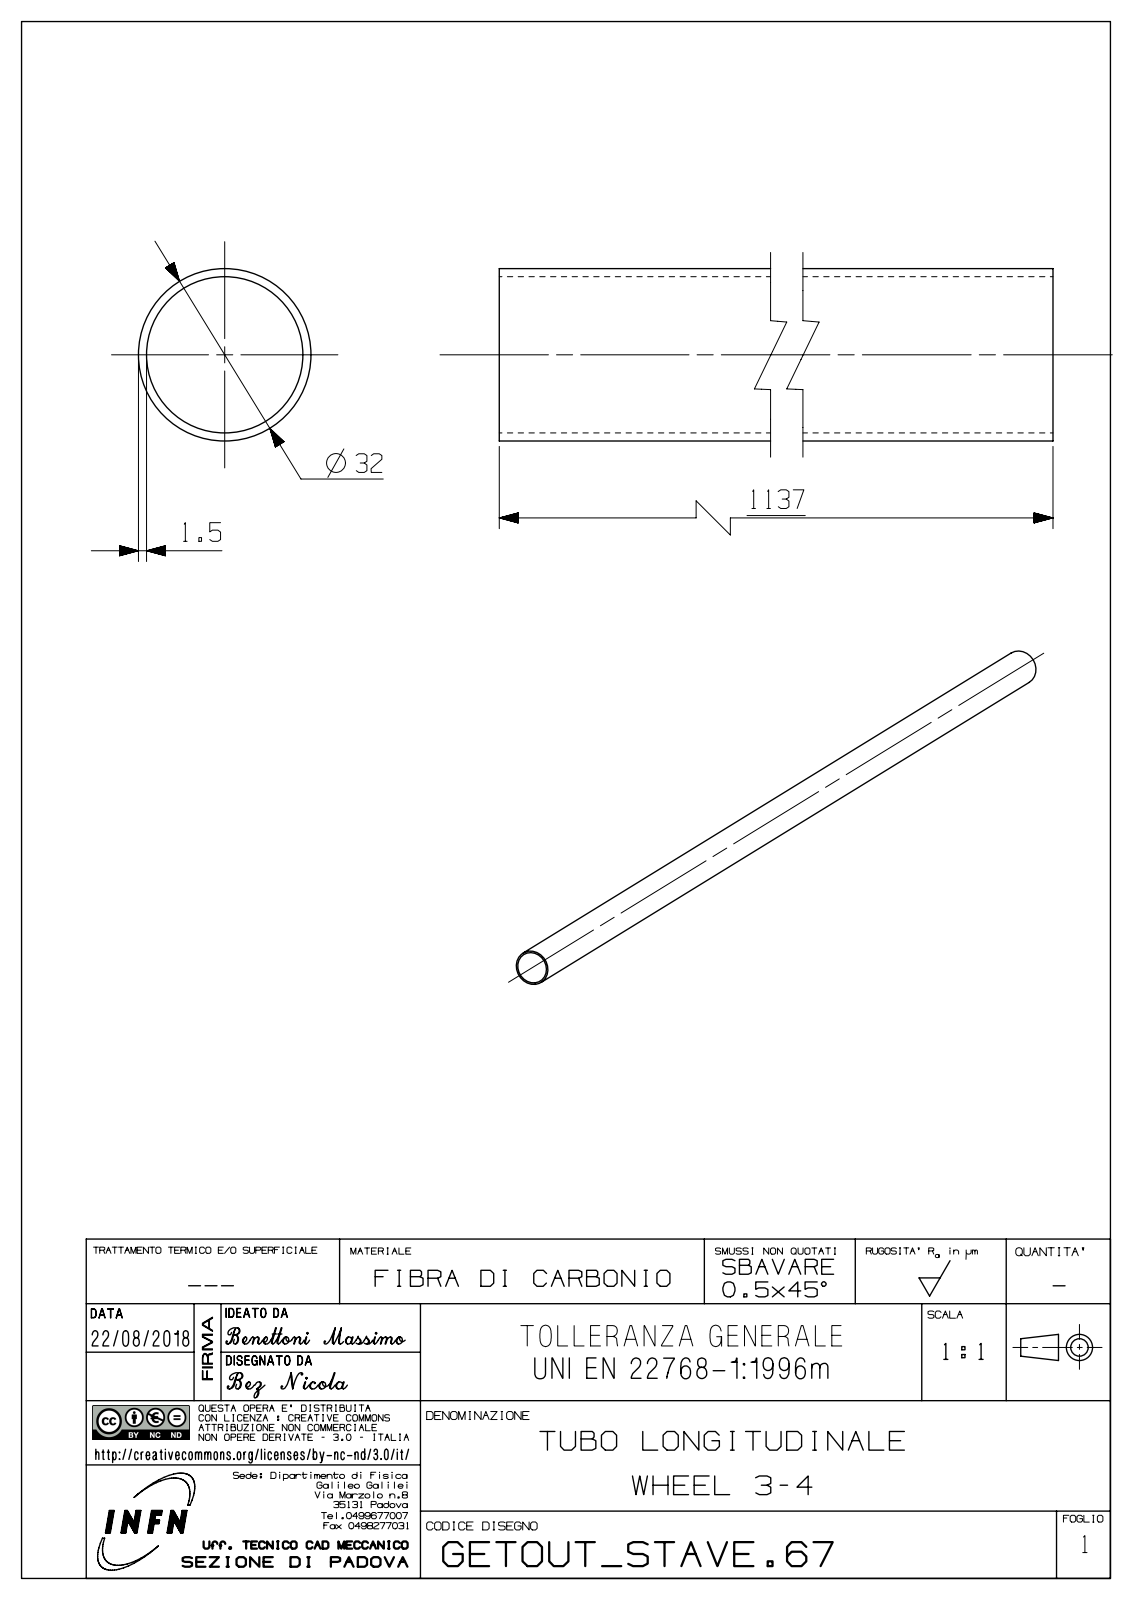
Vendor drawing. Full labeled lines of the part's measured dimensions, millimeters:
Part name (STEP PRODUCT): bez8324385A6uw3
STEP written by: SIEMENS PLM Software NX 12.0 (AUTOMOTIVE_DESIGN)
Units: millimetres
Bodies: 1 solid, 4 faces (2 planar, 2 cylindrical, 0 other)
Overall size (bounding box): 1137 × 32 × 32
Volume: 163 419 mm³ · Surface area: 218 179 mm²
Round holes (diameter × count): ⌀29 ×1
Round bosses / shafts (diameter × count): ⌀32 ×1
Main face-to-face distances: 1137
